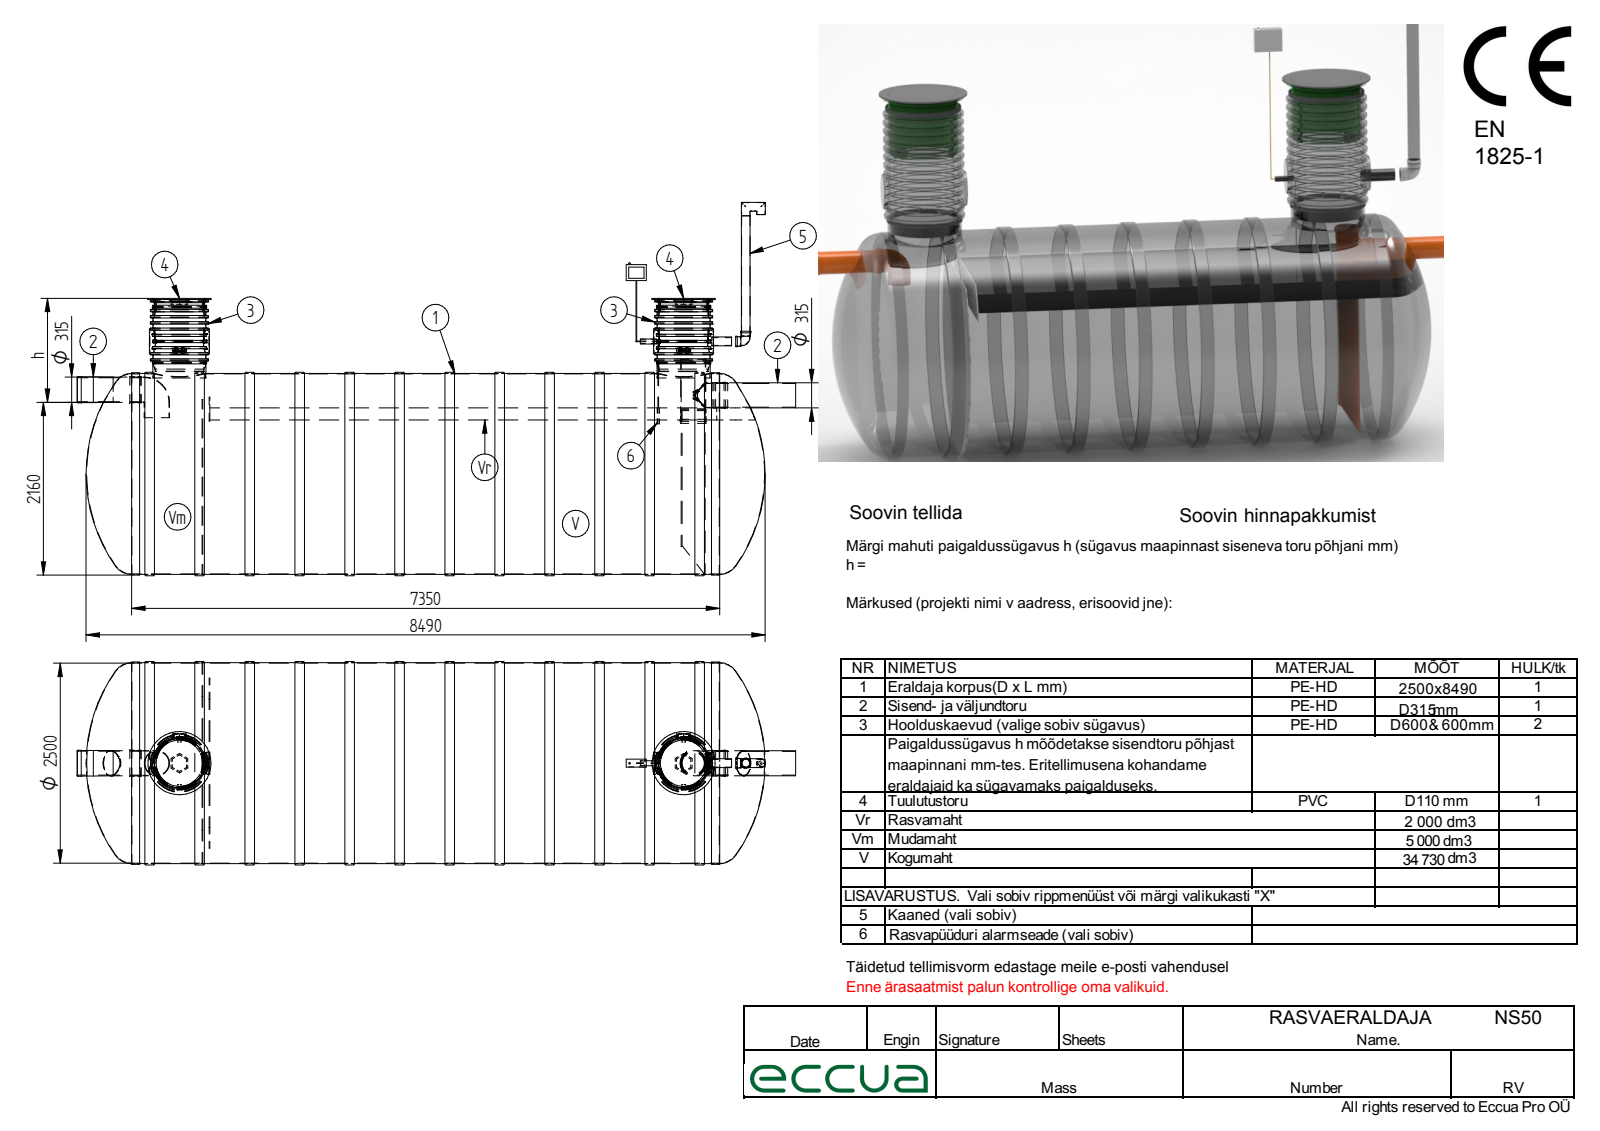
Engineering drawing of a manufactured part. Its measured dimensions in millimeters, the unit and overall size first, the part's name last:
Units: millimetres
Overall size (bounding box): 8983 × 4665.5 × 2542
Round holes (diameter × count): ⌀10 ×31, ⌀103.2 ×3, ⌀6 ×2, ⌀100 ×2, ⌀305 ×2, ⌀595 ×2, ⌀600 ×2, ⌀609 ×2, ⌀615 ×2, ⌀630 ×2, ⌀632.5 ×2, ⌀655 ×2
Round bosses / shafts (diameter × count): ⌀315 ×4, ⌀110 ×4, ⌀8.5 ×3, ⌀790 ×2, ⌀725 ×2, ⌀678.5 ×2, ⌀665 ×2, ⌀650 ×2
Partial cylindrical surfaces — rounded edges, fillets, slot ends (radius × count): R5 ×8, R30 ×8, R35 ×8, R3 ×6, R135 ×2, R140 ×2, R289.9 ×2, R151.3 ×1
Main face-to-face distances: 150, 8, 55, 95, 88, 5, 1465, 1520, 1370, 40
Hole centre spacings: 40, 49.88, 72.08, 34.71, 62.55, 26.75, 78, 17.81
Volume: 37 640 000 000 mm³ · Surface area: 321 700 000 mm²
Bodies: 53 solids, 1134 faces (442 planar, 356 cylindrical, 336 other)
Part name (STEP PRODUCT): Rasvaeraldaja NS50; Rasvaeraldaja NS65 ots1; Rasvaeraldaja NS50_silinder_D2500; Rasvaeraldaja NS65 ots2 (+8 more)
STEP written by: Solid Edge (AUTOMOTIVE_DESIGN)
